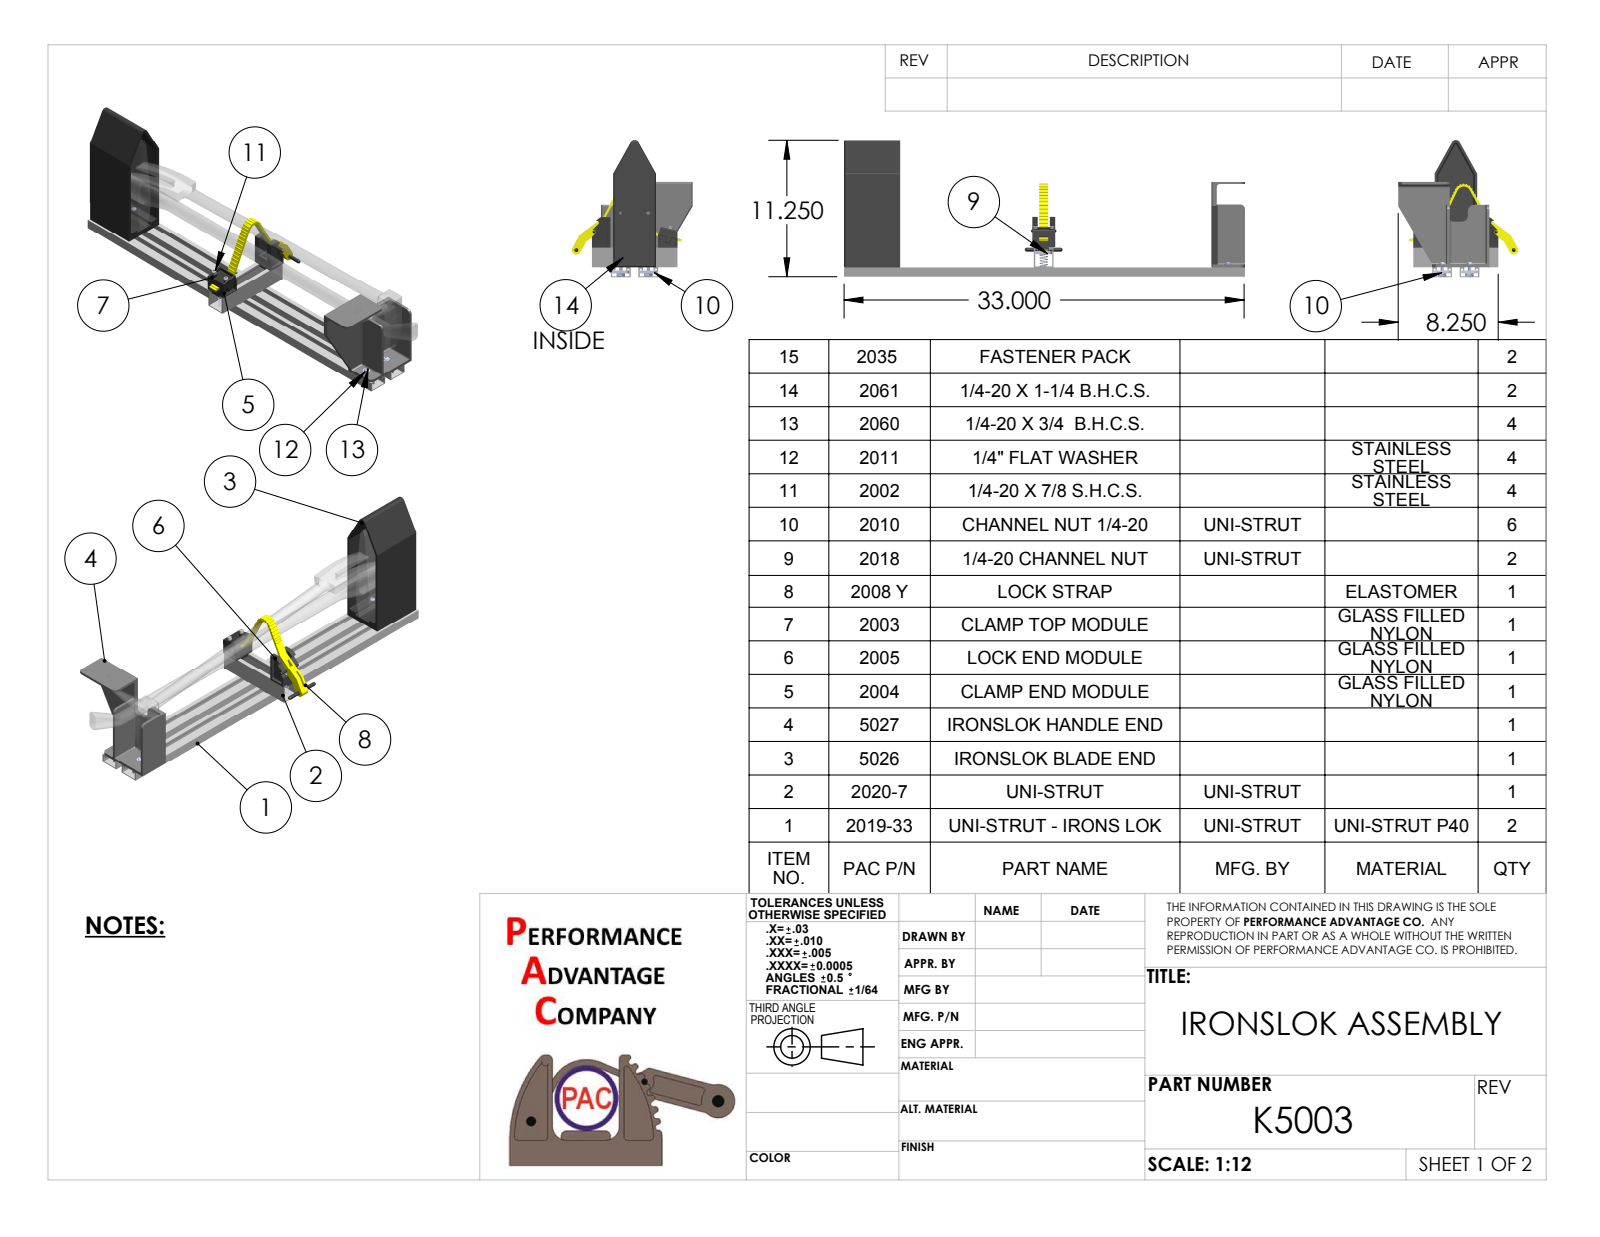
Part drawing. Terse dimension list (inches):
name: 2019-33; 2020-7; 5026; 5027 (+8 more)
written by: SolidWorks 2010 (CONFIG_CONTROL_DESIGN)
unit: in
bodies: 35 solids, 1758 faces (820 planar, 483 cylindrical, 455 other)
size: 36.125 × 11.25 × 9.893
volume: 200.4 in³; area: 1 581 in²
holes: 10× ⌀0.201, 6× ⌀0.281, 4× ⌀0.288, 2× ⌀0.25, 2× ⌀0.332, 1× ⌀0.26, 1× ⌀0.291, 1× ⌀0.625, 1× ⌀0.64
bosses: 11× ⌀0.25, 6× ⌀0.437, 4× ⌀0.625, 4× ⌀0.375, 1× ⌀1, 1× ⌀0.313
rounds: 75× R0.031, 63× R0.125, 38× R0.062, 30× R0.02, 20× R0.063, 16× R0.424, 8× R0.06, 8× R0.25
face distances: 0.813, 2.25, 0.078, 1.516, 0.109, 0.735, 0.219, 0.406, 0.218, 1.219
hole spacings: 2.25, 2.252, 14.125, 14.218, 14.303, 15.187, 15.274, 15.353
